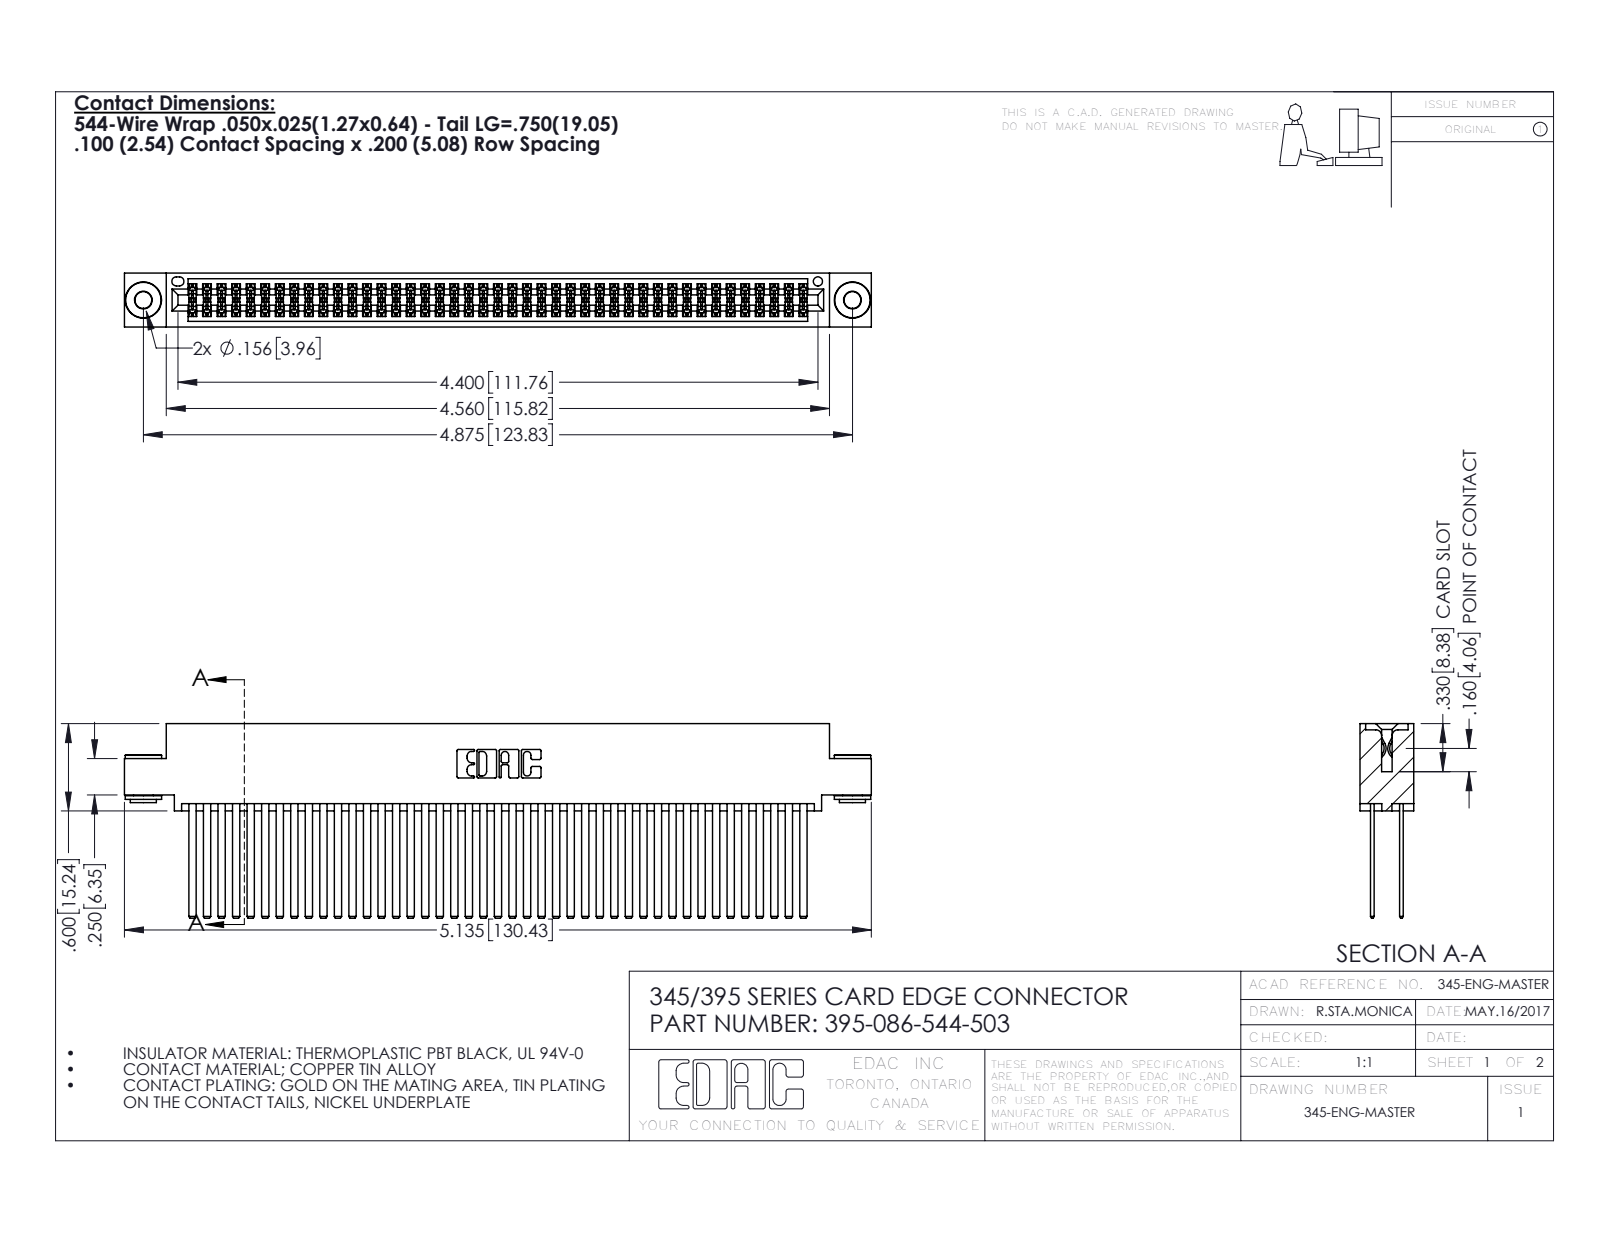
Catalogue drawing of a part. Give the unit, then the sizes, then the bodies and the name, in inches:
Units: inches
Overall size (bounding box): 5.135 × 1.337 × 0.37
Round holes (diameter × count): ⌀0.116 ×2, ⌀0.156 ×2, ⌀0.064 ×1
Round bosses / shafts (diameter × count): ⌀0.25 ×2, ⌀0.18 ×2, ⌀0.136 ×2
Partial cylindrical surfaces — rounded edges, fillets, slot ends (radius × count): R0.006 ×129, R0.01 ×22, R0.007 ×6, R0.031 ×6, R0.026 ×3, R0.014 ×2, R0.019 ×2, R0.022 ×2
Main face-to-face distances: 0.2, 0.025, 0.072, 0.098, 0.272, 0.298, 0.225, 0.175, 0.37, 0.05
Hole centre spacings: 0.27, 4.639, 4.875
Volume: 0.844 in³ · Surface area: 37.66 in²
Bodies: 89 solids, 3952 faces (2588 planar, 1356 cylindrical, 8 other)
Part name (STEP PRODUCT): 395-086-544-503; 345-292-001_345-293-144; 345-250-002_345-250-002-102; 345 Part_0.110 Offset - 0.156 Dia-TH
STEP written by: SolidWorks 2016 (CONFIG_CONTROL_DESIGN)
